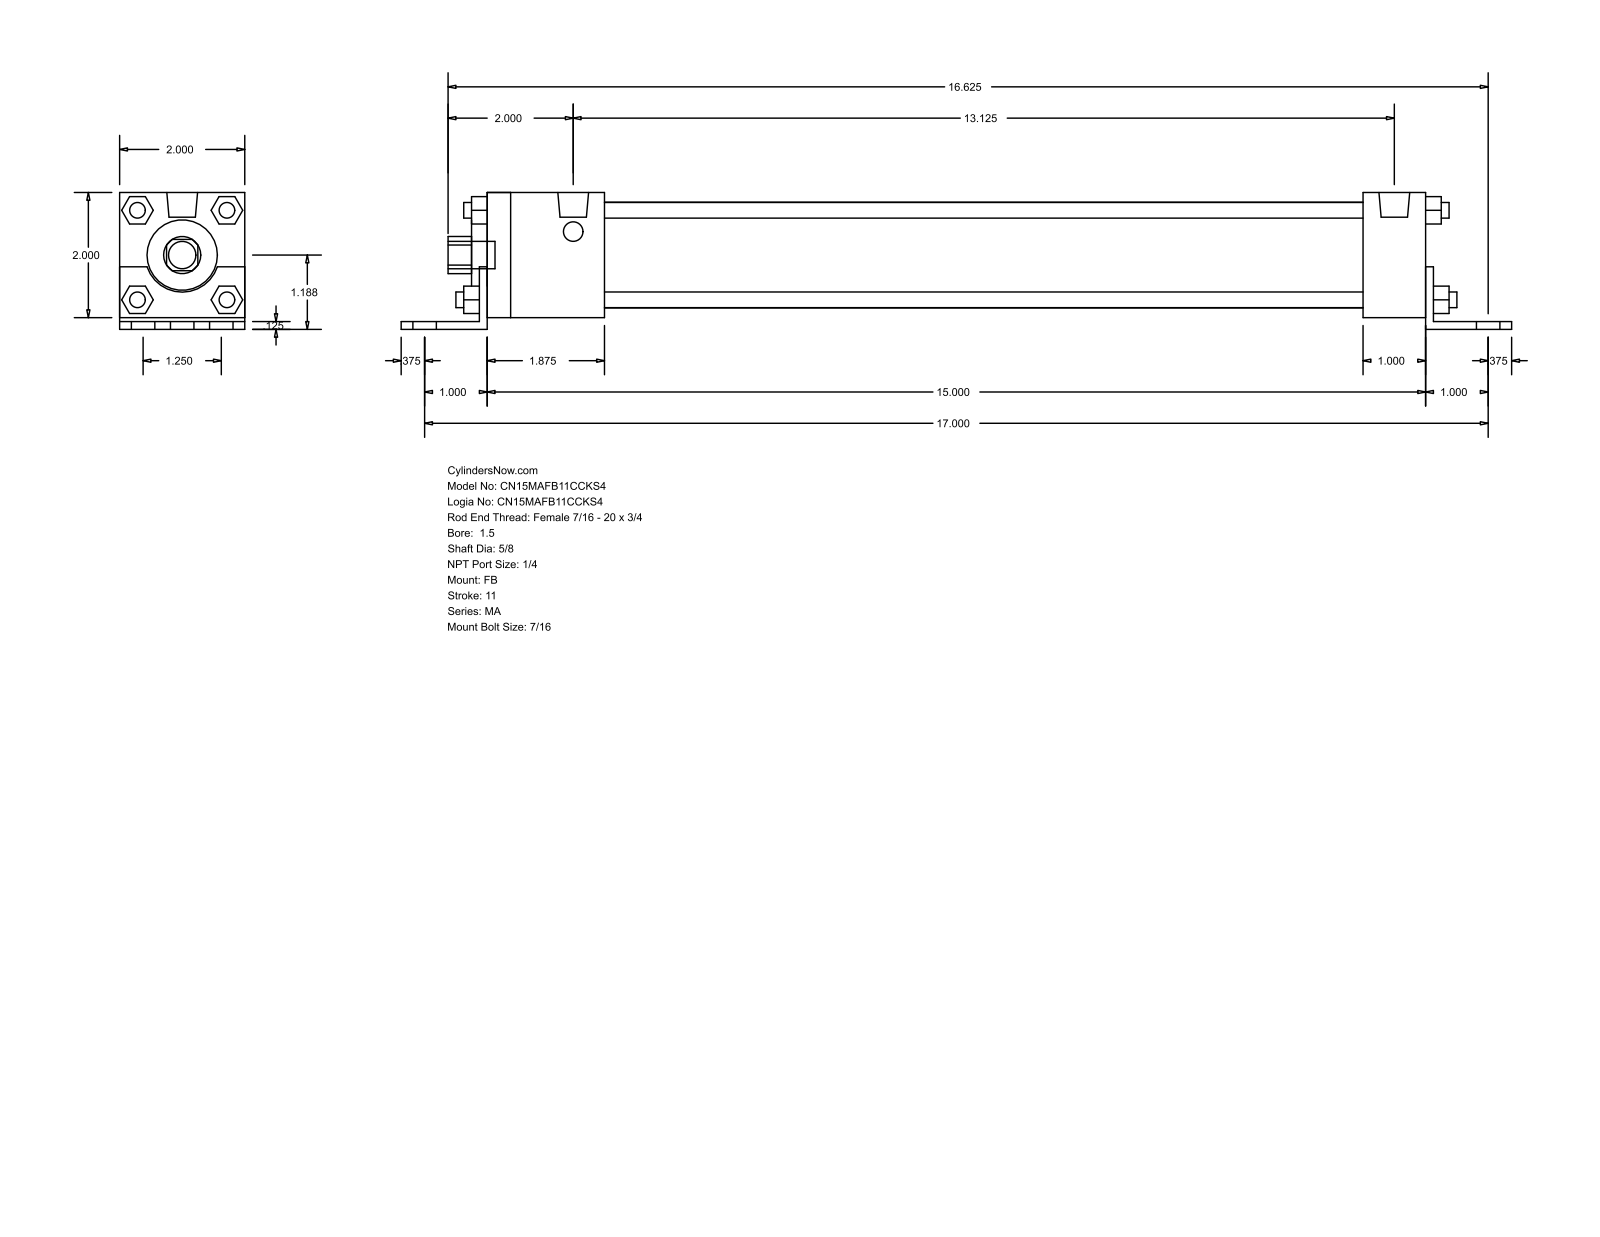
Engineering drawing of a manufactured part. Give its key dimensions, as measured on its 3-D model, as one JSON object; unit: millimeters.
{"part_name": "MA_FB__0150_0.625", "step_written_by": "GSSL Pune (CONFIG_CONTROL_DESIGN)", "units": "millimeters", "bodies": {"solids": 0, "faces": 140, "planar": 105, "cylindrical": 35, "other": 0}, "overall_size": [450.85, 55.56, 50.8], "round_holes": [[15.88, 1], [28.57, 1], [42.93, 1]], "round_bosses_or_shafts": [[11.11, 7], [7.94, 4], [6.35, 4], [12.49, 2]], "partial_cylinders_radius": [[7.54, 1], [15.05, 1]], "face_to_face_distances": [50.8, 3.17, 4.76, 55.56, 1.59, 52.39, 25.4, 387.35, 6.35, 381]}
